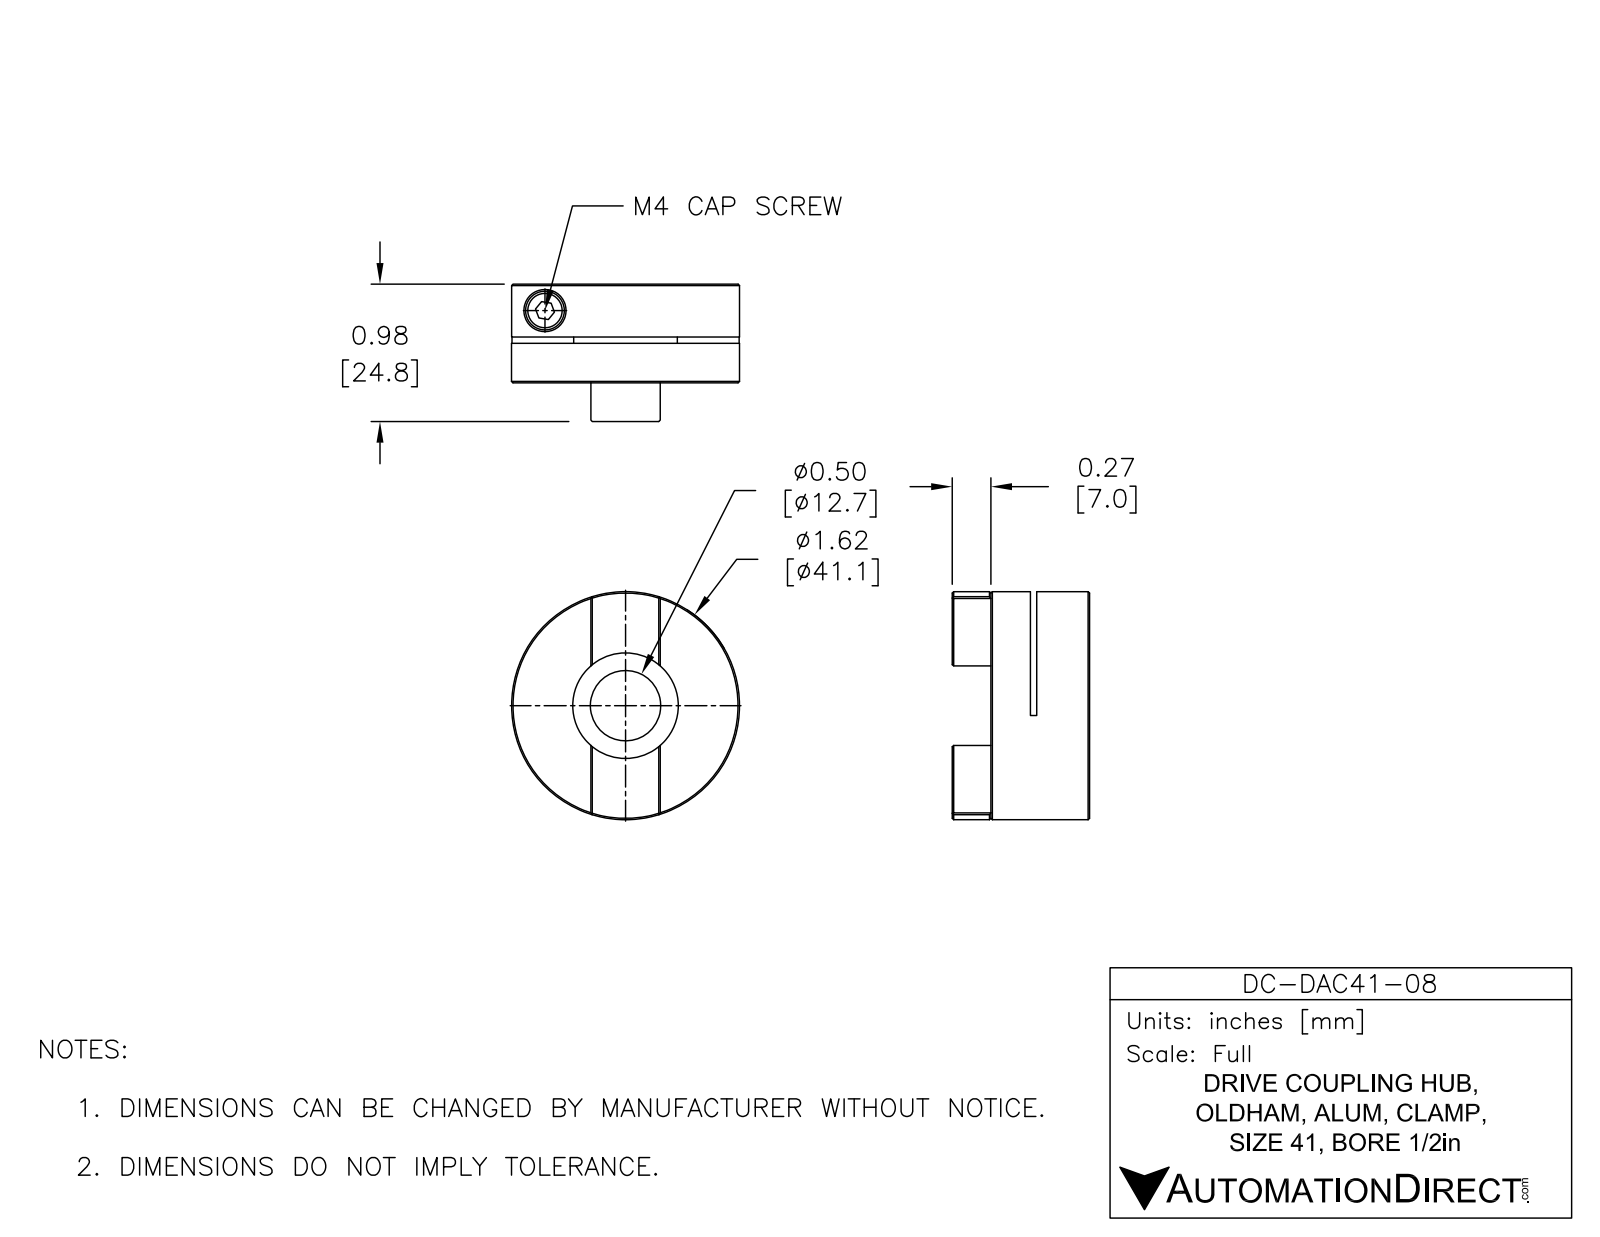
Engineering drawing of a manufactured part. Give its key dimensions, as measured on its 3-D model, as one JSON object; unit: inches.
{"part_name": "DC-DAC41-08", "step_written_by": "SolidWorks 2015 (AUTOMOTIVE_DESIGN)", "units": "inches", "bodies": {"solids": 1, "faces": 60, "planar": 34, "cylindrical": 16, "other": 10}, "overall_size": [1.62, 1.62, 0.976], "volume_in3": 1.351, "surface_area_in2": 12.36, "round_holes": [[0.157, 1], [0.3, 1], [0.5, 1], [0.625, 1]], "round_bosses_or_shafts": [[1.62, 1]], "face_to_face_distances": [0.701, 0.281, 0.42, 0.326, 0.045, 0.375, 0.274, 0.556, 0.6, 0.975]}
